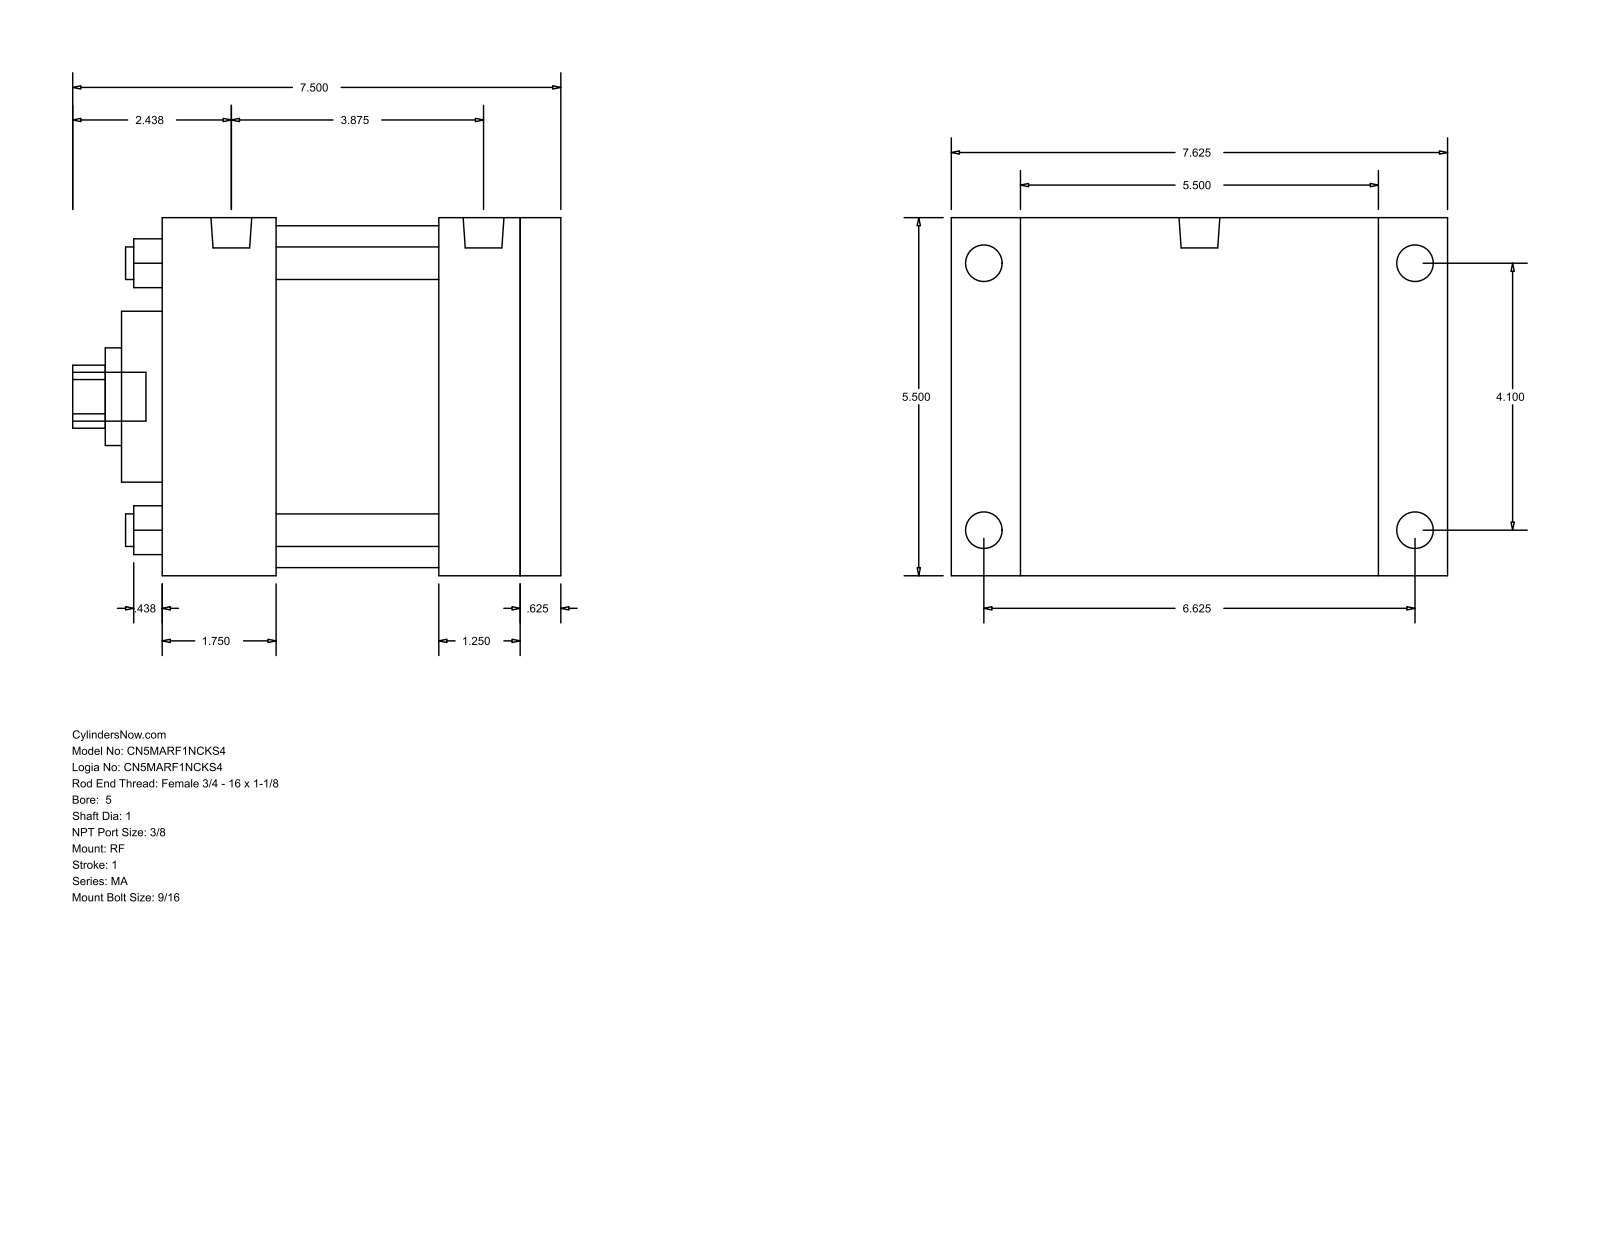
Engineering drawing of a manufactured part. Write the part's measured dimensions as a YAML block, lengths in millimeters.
part_name: "MA_RF__0500_1"
step_written_by: "GSSL Pune (CONFIG_CONTROL_DESIGN)"
units: millimeters
bodies: {solids: 0, faces: 94, planar: 65, cylindrical: 29, other: 0}
overall_size: [193.68, 190.5, 139.7]
round_holes:
  - {diameter: 12.7, count: 4}
  - {diameter: 25.4, count: 1}
  - {diameter: 38.1, count: 1}
  - {diameter: 66.67, count: 1}
  - {diameter: 133.35, count: 1}
round_bosses_or_shafts:
  - {diameter: 14.29, count: 4}
  - {diameter: 11.11, count: 4}
  - {diameter: 15.93, count: 2}
  - {diameter: 19.05, count: 1}
partial_cylinders:
  - {radius: 12.29, count: 1}
face_to_face_distances: [139.7, 155.58, 15.88, 166.69, 44.46, 95.24, 111.12, 107.96, 63.5, 31.74]
hole_center_spacings: [73.64, 104.14, 147.28]
